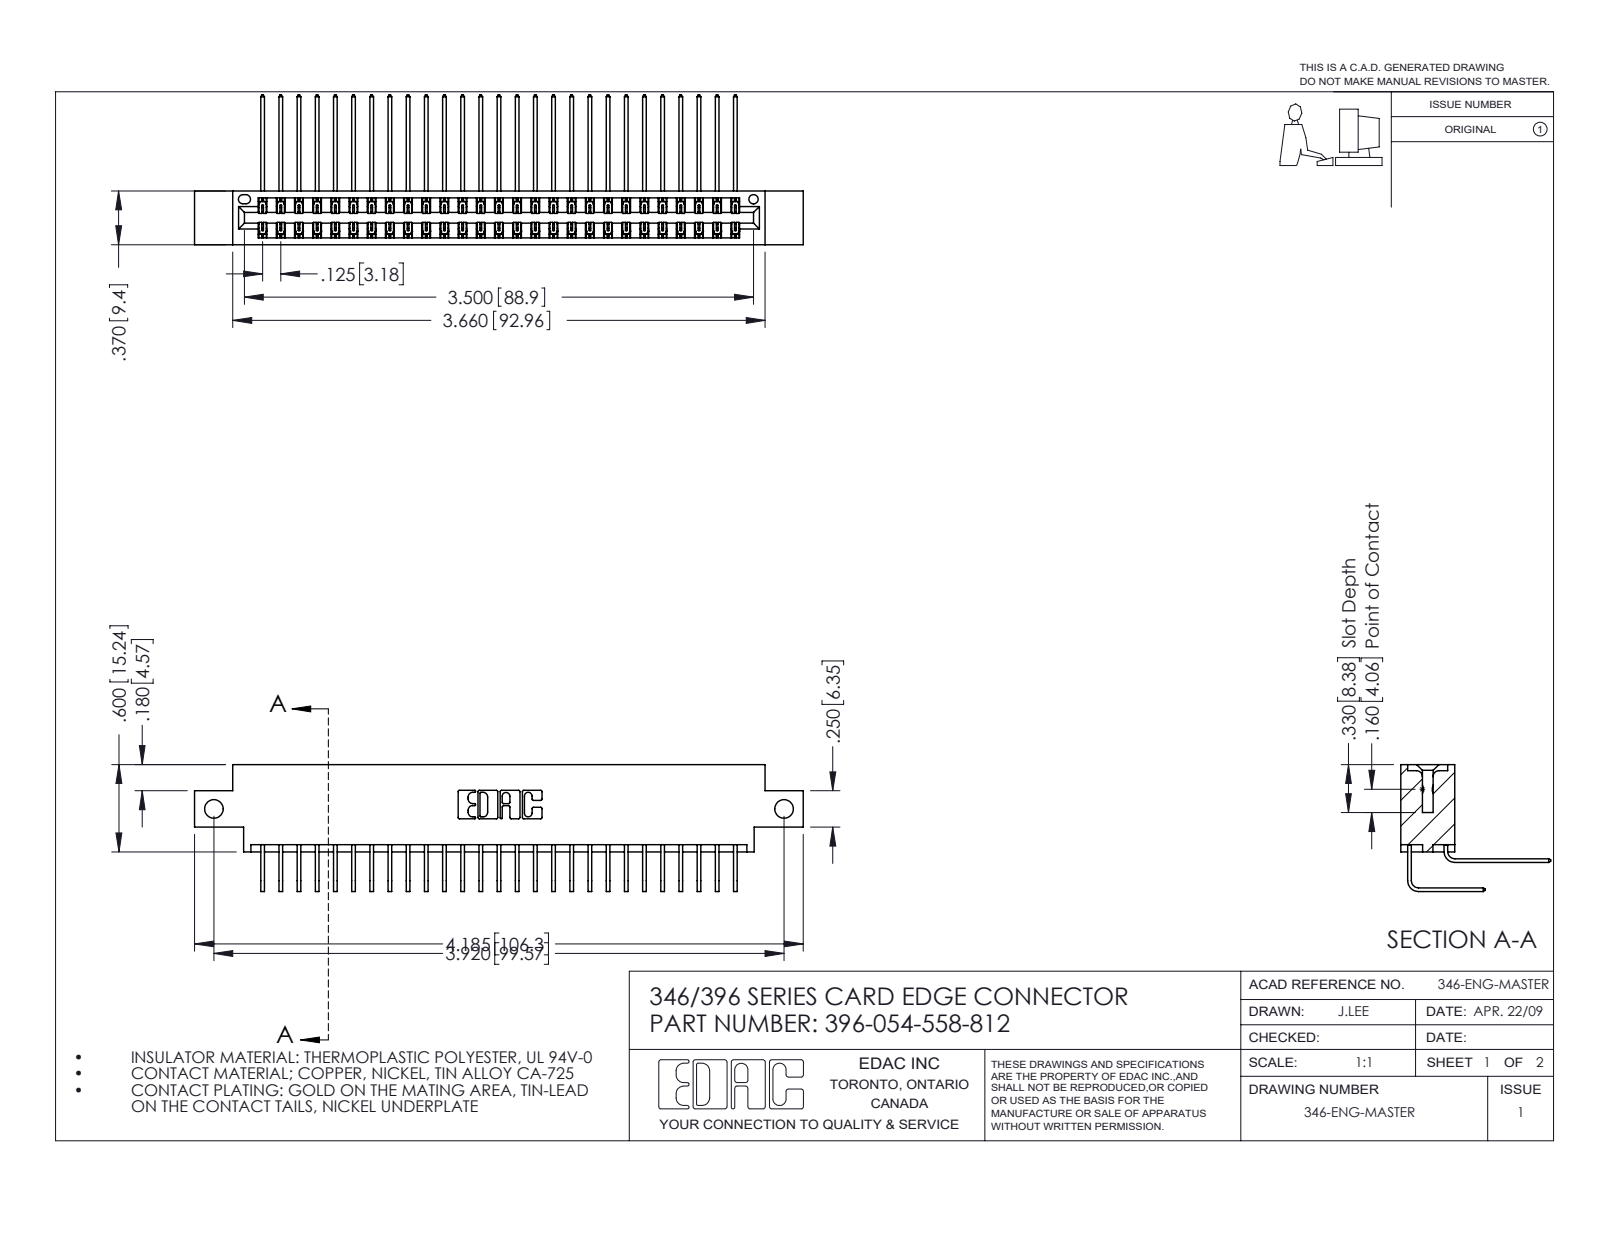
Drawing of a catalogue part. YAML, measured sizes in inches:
part_name: "345-292-001_558 559 Tail - 1; 396-054-558-812; 346 Part_0.170 Offset - Side Mount; 345-292-001_558 Tail - 2"
step_written_by: "SolidWorks 2016 (CONFIG_CONTROL_DESIGN)"
units: inches
bodies: {solids: 55, faces: 3042, planar: 2078, cylindrical: 964, other: 0}
overall_size: [4.185, 1.03, 0.873]
volume: 0.63
surface_area: 24
round_holes:
  - {diameter: 0.128, count: 2}
  - {diameter: 0.064, count: 1}
partial_cylinders:
  - {radius: 0.006, count: 81}
  - {radius: 0.01, count: 22}
  - {radius: 0.007, count: 6}
  - {radius: 0.031, count: 6}
  - {radius: 0.026, count: 3}
  - {radius: 0.014, count: 2}
  - {radius: 0.022, count: 2}
  - {radius: 0.024, count: 2}
face_to_face_distances: [0.322, 0.048, 0.025, 0.37, 0.25, 0.298, 0.072, 0.275, 0.148, 0.222]
hole_center_spacings: [3.92]
